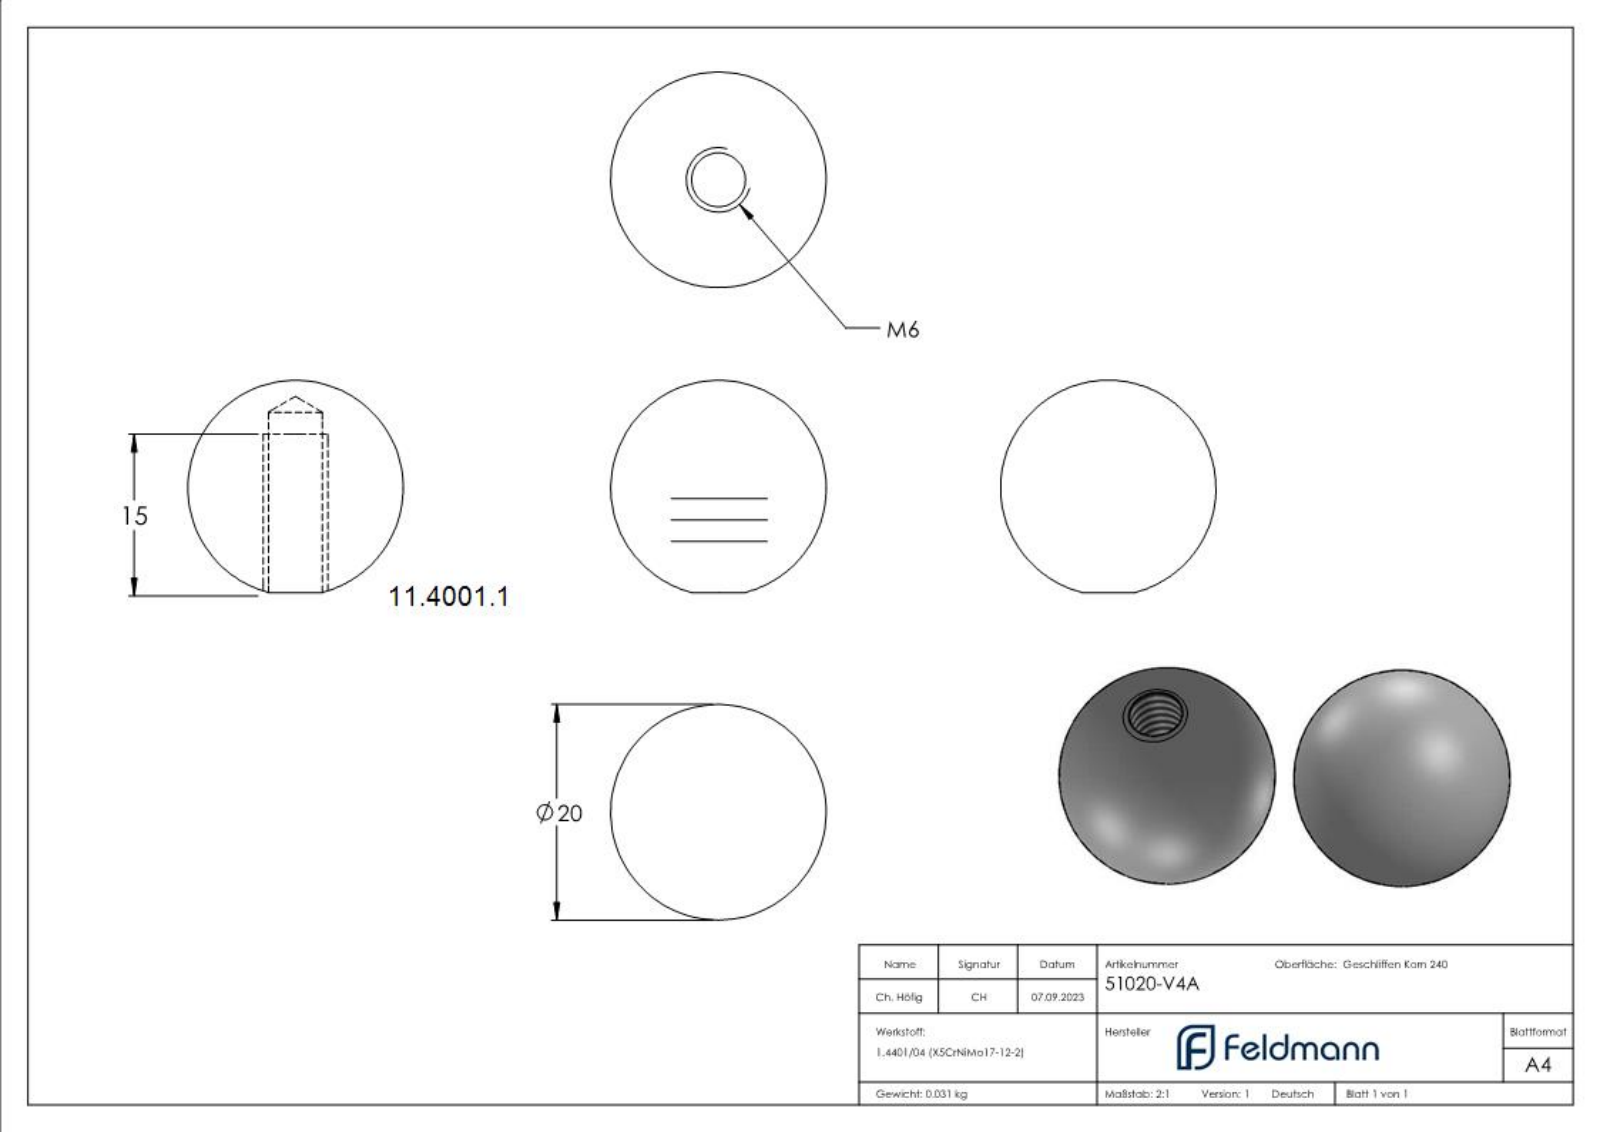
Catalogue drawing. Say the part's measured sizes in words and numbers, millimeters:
The part is named "51020-V4A". Its 3-D file was written by "SolidWorks 2018 (CONFIG_CONTROL_DESIGN)". It is 1 solid with 3 faces: 0 planar, 1 cylindrical and 2 other. Overall it measures 20 by 20 by 19.68 millimeters. Its volume is 3 848 cubic millimeters and its surface area 1 522 square millimeters. Round holes: 1 of diameter 5.
